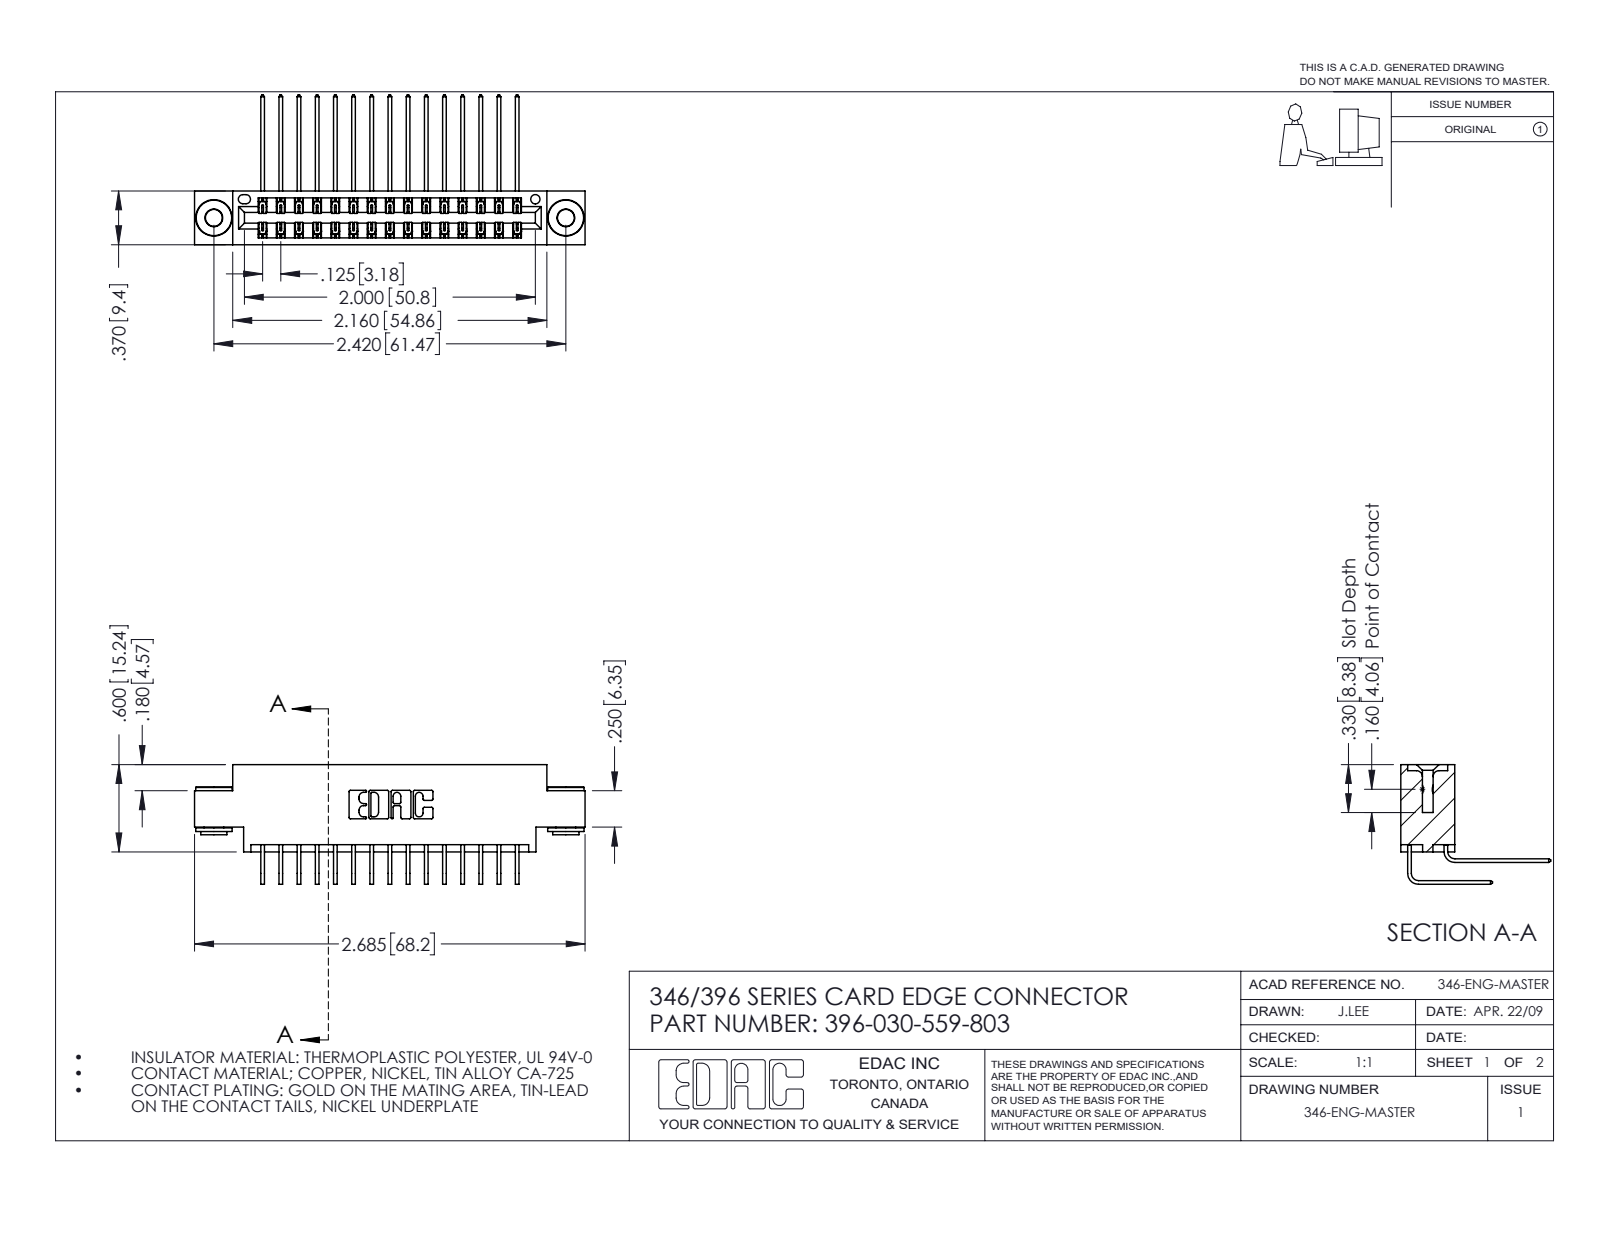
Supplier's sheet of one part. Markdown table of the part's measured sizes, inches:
| quantity | value |
| --- | --- |
| part name | 345-292-001_559 Tail - 2; 345-250-002_345-250-002-102; 345-292-001_558 559 Tail - 1; 396-030-559-803 (+1 more) |
| STEP written by | SolidWorks 2016 (CONFIG_CONTROL_DESIGN) |
| units | inches |
| bodies | 33 solids, 1784 faces (1200 planar, 576 cylindrical, 8 other) |
| overall size | 2.685 × 1.03 × 0.823 |
| volume | 0.395 in³ |
| surface area | 15.04 in² |
| round holes (diameter × count) | 0.116 × 2, 0.156 × 2, 0.064 × 1 |
| round bosses / shafts (diameter × count) | 0.25 × 2, 0.18 × 2, 0.136 × 2 |
| partial cylindrical surfaces (radius × count) | 0.006 × 45, 0.01 × 22, 0.007 × 6, 0.031 × 6, 0.026 × 3, 0.014 × 2, 0.022 × 2, 0.024 × 2 |
| main face-to-face distances | 0.048, 0.322, 0.37, 0.25, 0.025, 0.072, 0.298, 0.275, 0.15, 0.148 |
| hole center spacings | 0.246, 2.213, 2.42 |
